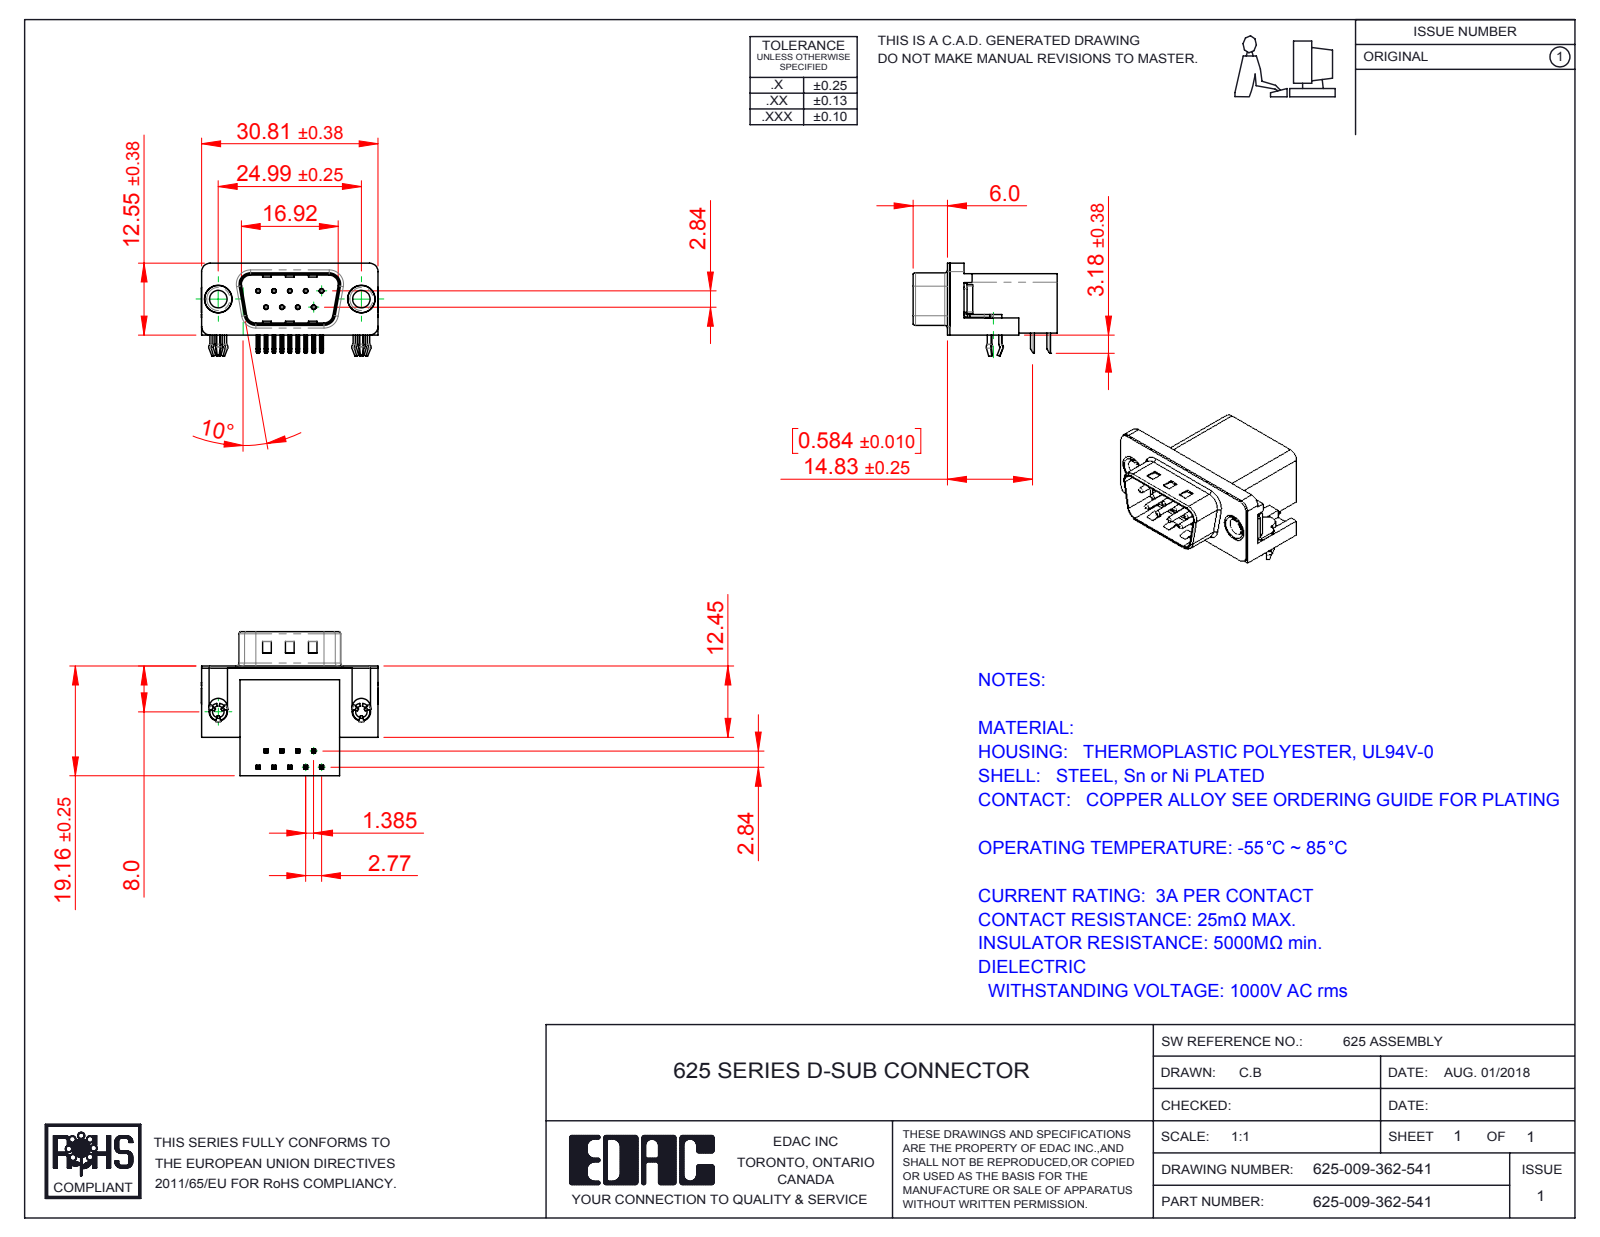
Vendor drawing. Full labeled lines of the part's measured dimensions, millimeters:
Part name (STEP PRODUCT): 625 Contact Bottom; 625 Thru Hole Rivet; 625 Housing_9 Socket; 625 3 Prong Board Lock (+3 more)
STEP written by: SolidWorks 2016 (CONFIG_CONTROL_DESIGN)
Units: millimetres
Bodies: 15 solids, 1057 faces (611 planar, 305 cylindrical, 141 other)
Overall size (bounding box): 30.89 × 25.16 × 16.25
Volume: 4 472 mm³ · Surface area: 4 989 mm²
Round holes (diameter × count): ⌀0.35 ×9, ⌀0.8 ×9, ⌀2 ×2, ⌀3.05 ×2, ⌀4 ×2, ⌀4.8 ×2, ⌀5 ×2
Round bosses / shafts (diameter × count): ⌀0.75 ×9, ⌀4.9 ×2, ⌀4.75 ×2, ⌀3.85 ×2, ⌀3 ×2
Partial cylindrical surfaces — rounded edges, fillets, slot ends (radius × count): R0.25 ×48, R0.12 ×18, R1 ×16, R0.5 ×9, R1.5 ×8, R1.6 ×8, R0.9 ×4, R2 ×4
Main face-to-face distances: 0.4, 10.34, 18.76, 19.16, 2.9, 16.26, 2.5, 0.35, 10.69, 6.7
Hole centre spacings: 3.16, 2.77, 5.54, 5.03, 5.04, 8.31, 7.48, 7.49
